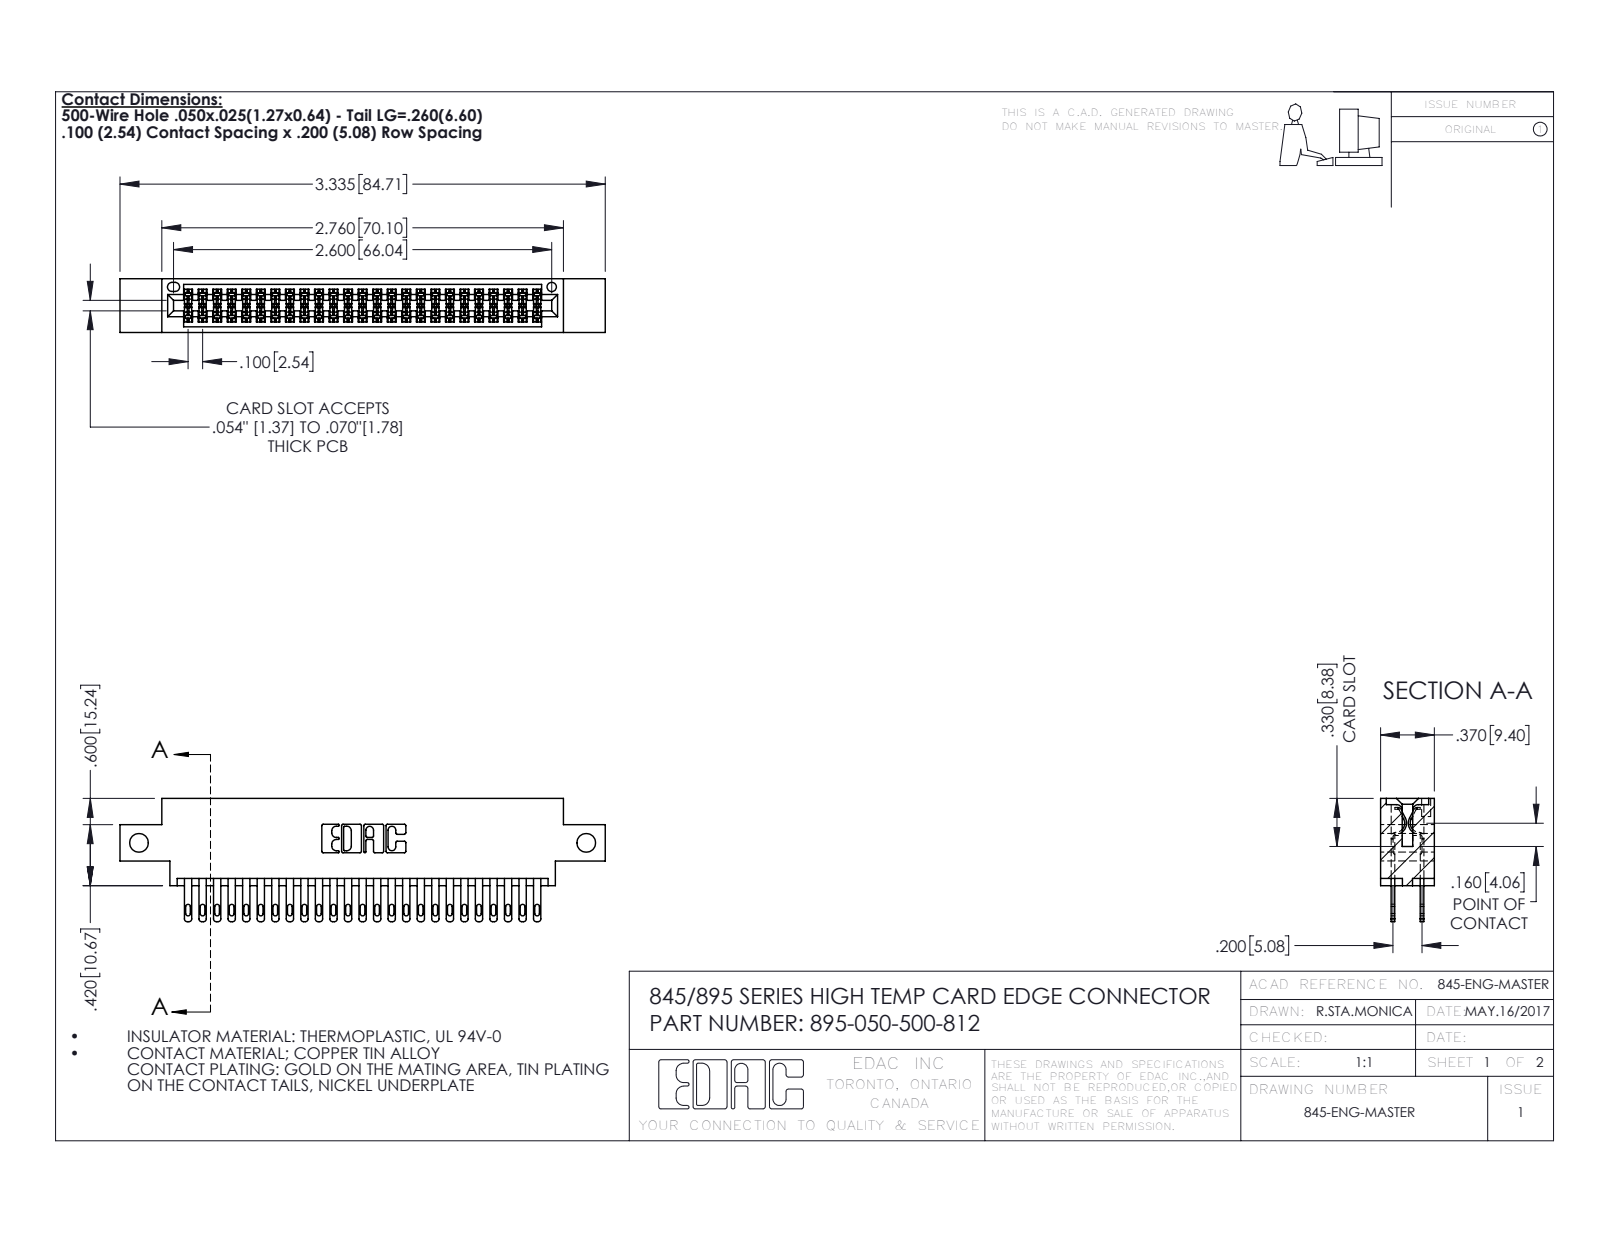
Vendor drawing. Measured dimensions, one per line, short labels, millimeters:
name: 895-050-500-812; 345-292-001_345-293-100; 845 Part_0.170 Offset - Side Mount
written by: SolidWorks 2020 (CONFIG_CONTROL_DESIGN)
unit: mm
bodies: 51 solids, 2430 faces (1434 planar, 996 cylindrical, 0 other)
size: 84.7 × 21.5 × 9.4
volume: 8 030 mm³; area: 12 050 mm²
holes: 2× ⌀3.3, 1× ⌀1.6
rounds: 75× R0.2, 50× R0.4, 50× R0.5, 22× R0.3, 6× R0.2, 6× R0.8, 3× R0.7, 2× R0.4
face distances: 7.6, 1.8, 5.1, 2.5, 6.9, 0.6, 9.4, 5.7, 4.4, 3.8
hole spacings: 78.1
